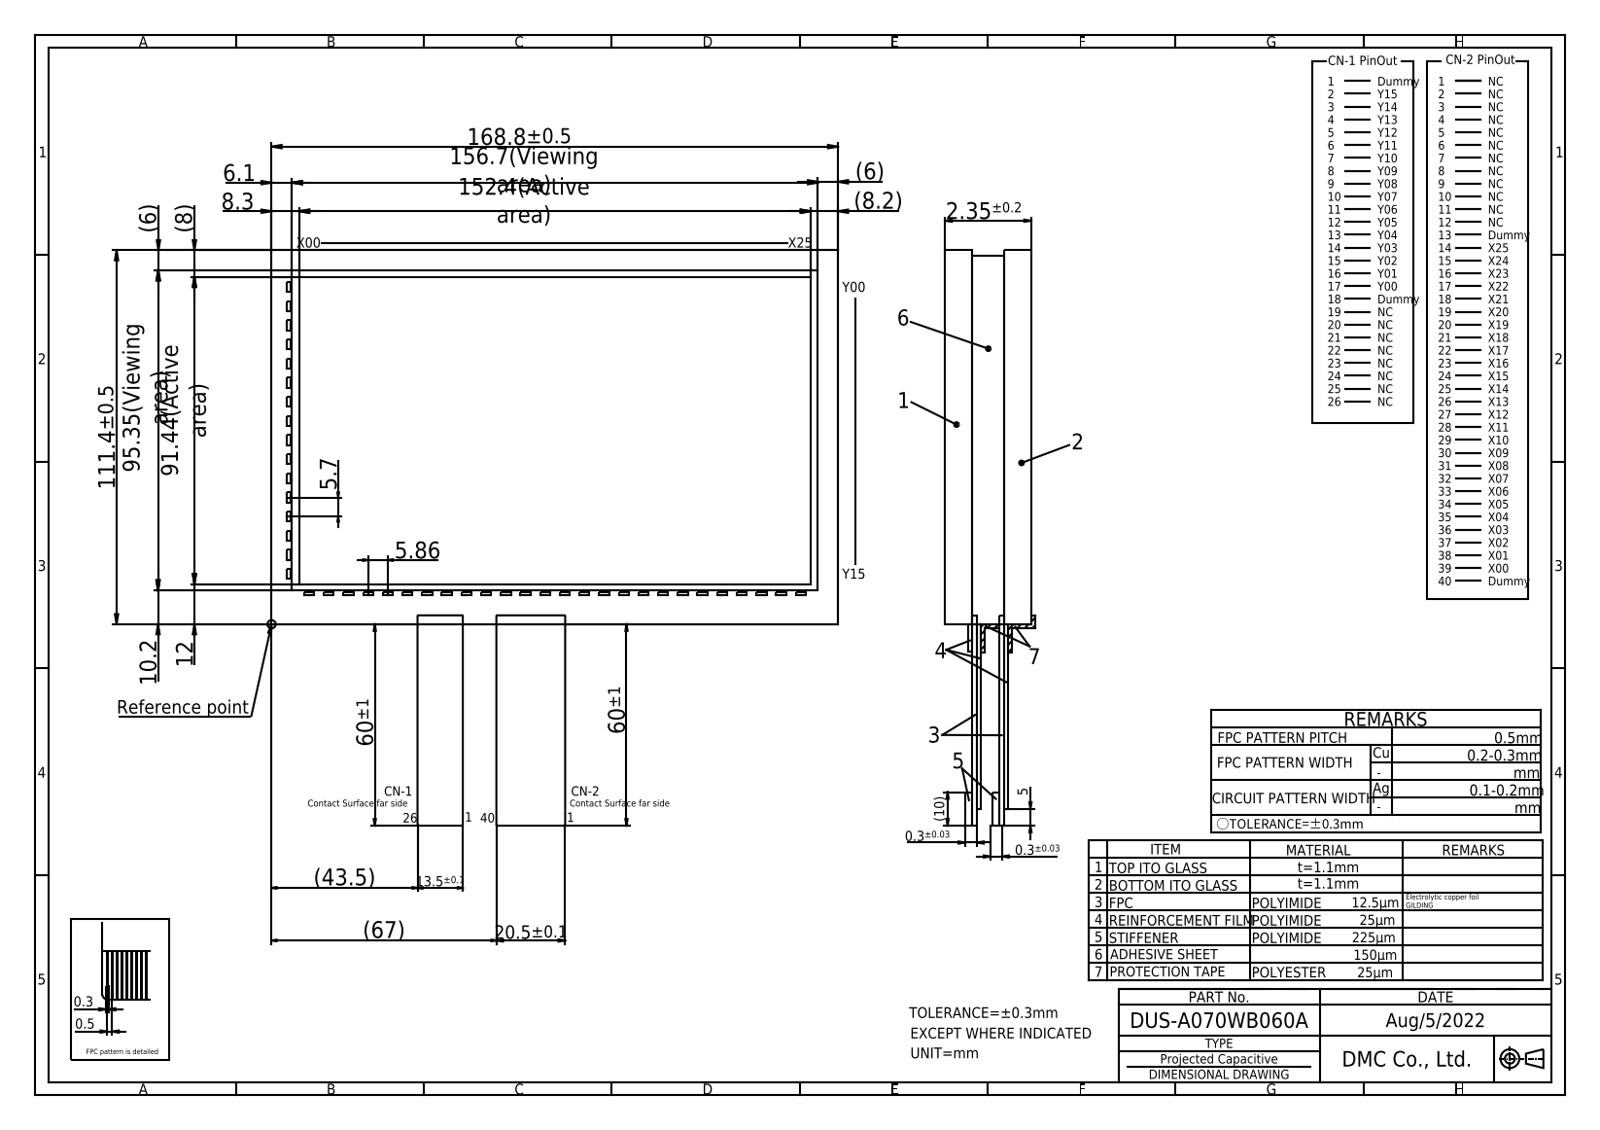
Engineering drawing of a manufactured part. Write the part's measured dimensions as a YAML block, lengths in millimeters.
part_name: "DUS-A070WB060A"
step_written_by: "Autodesk Inventor 2020 (CONFIG_CONTROL_DESIGN)"
units: millimeters
bodies: {solids: 1, faces: 302, planar: 298, cylindrical: 4, other: 0}
overall_size: [236.32, 193.68, 2.35]
volume: 44398
surface_area: 43168
partial_cylinders:
  - {radius: 0.2, count: 4}
face_to_face_distances: [2.35, 1.14, 1.21, 1.25, 1.1, 1.11, 1, 2.25, 111.4, 0.8]
